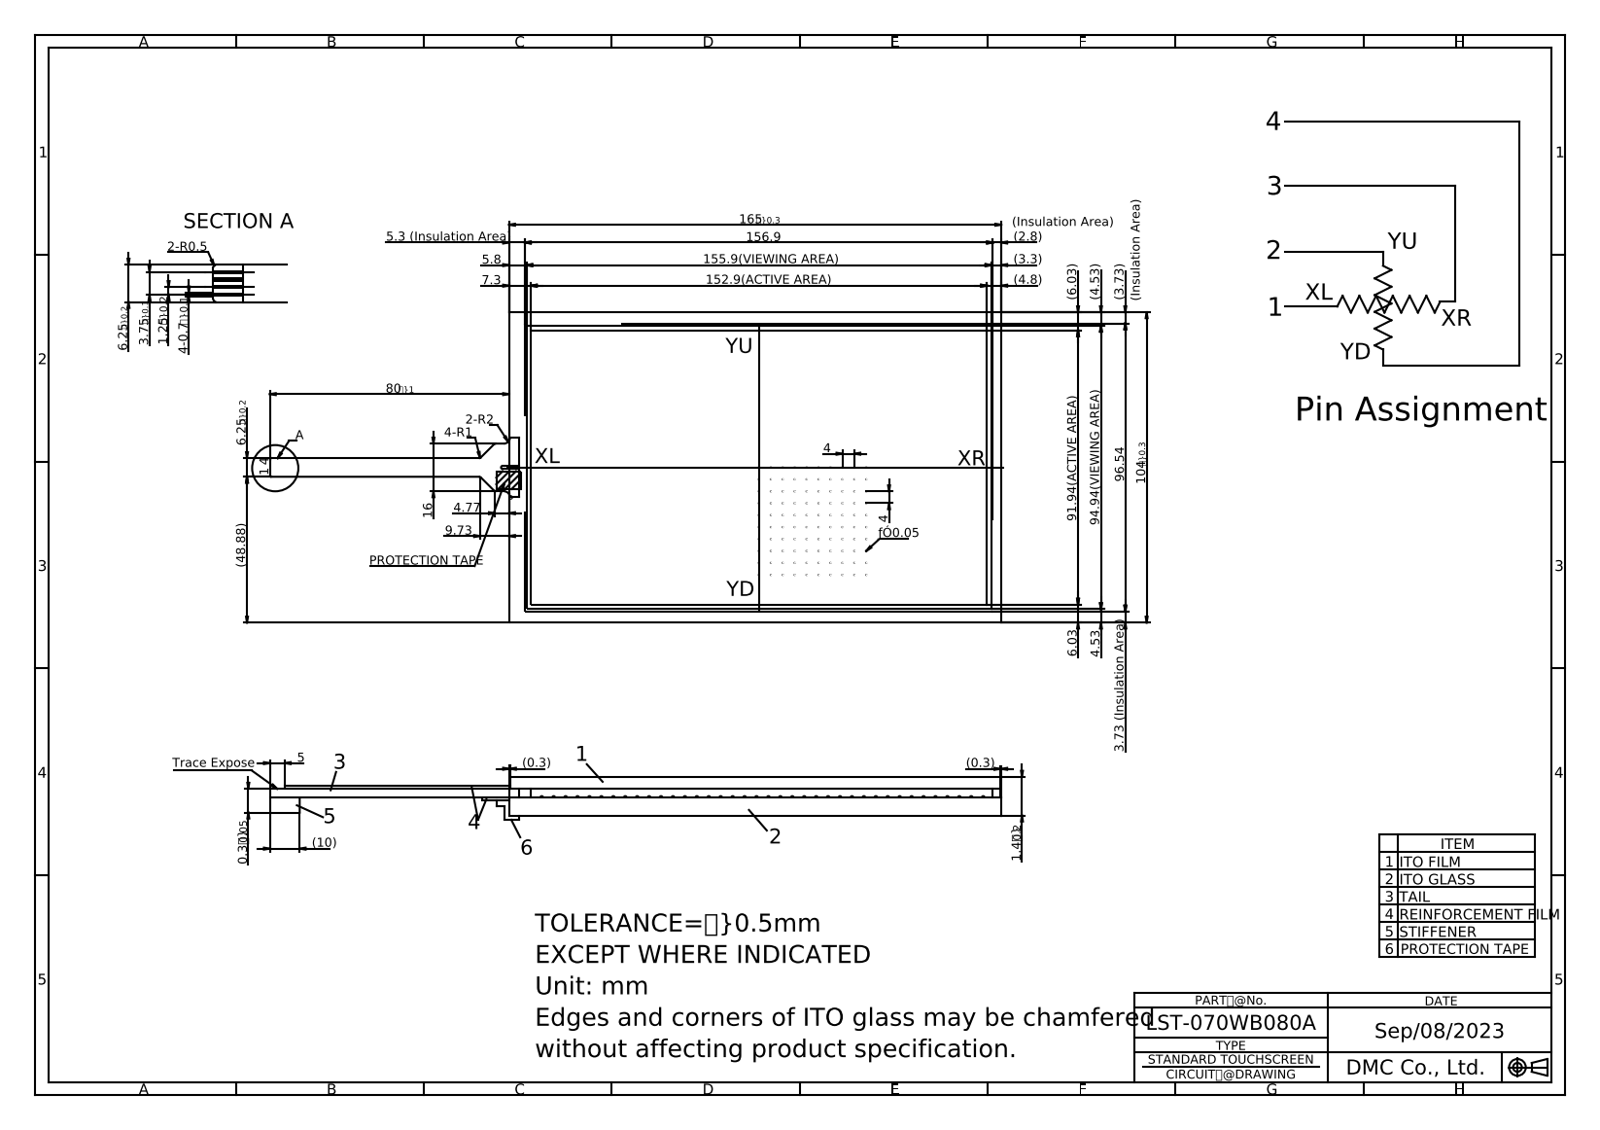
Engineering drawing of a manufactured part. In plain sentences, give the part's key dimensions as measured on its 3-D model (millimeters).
The part is named "LST-070WB080A". Its 3-D file was written by "Autodesk Inventor 2020 (CONFIG_CONTROL_DESIGN)". It is 1 solid with 51 faces: 45 planar, 6 cylindrical and 0 other. Overall it measures 245 by 104 by 1.4 millimeters. Its volume is 24 023 cubic millimeters and its surface area 36 342 square millimeters. Partial cylindrical surfaces (rounded edges, fillets, slot ends): 4 of radius 1, 2 of radius 0.5. The main face-to-face distances are 1.4, 1.3, 1.21, 1.11, 104, 165, 0.81, 0.4, 0.49, 0.59.
